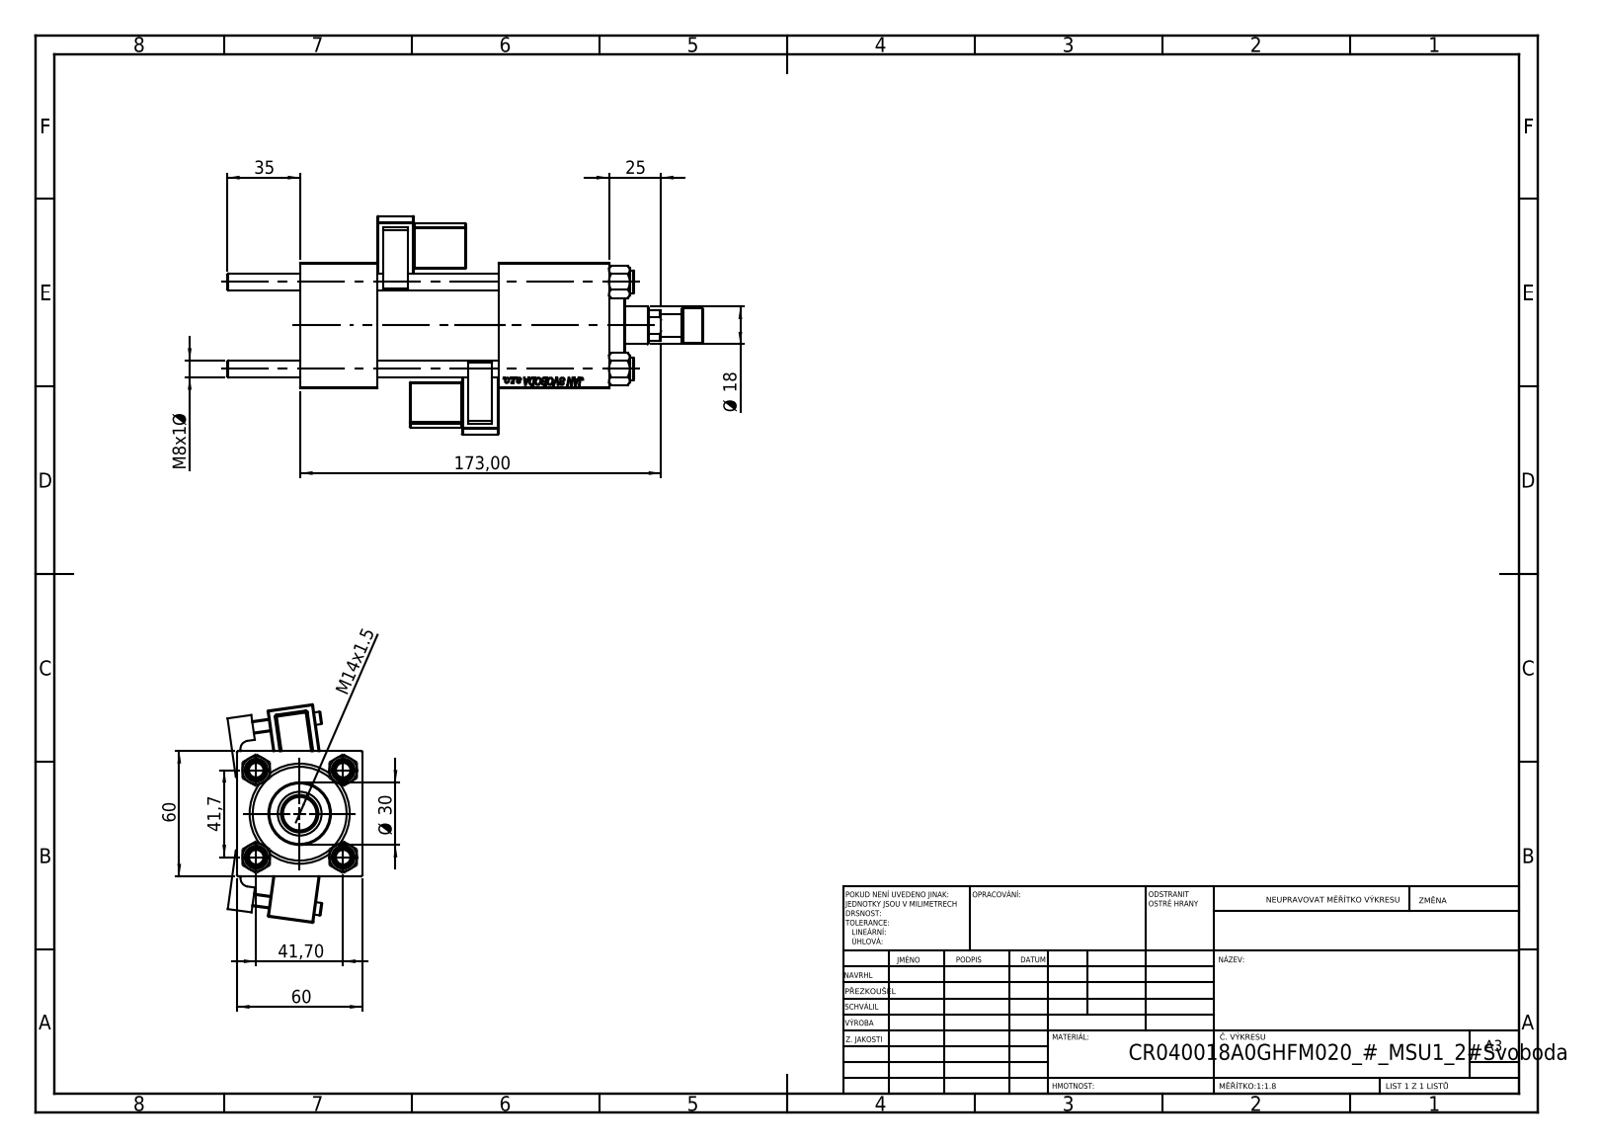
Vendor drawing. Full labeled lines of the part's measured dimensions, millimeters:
Part name (STEP PRODUCT): CR025_012_A_0_G_A_G_M_020_+#_##_TYCINKA; V215CR_MSU; V215CR_ROD_END_F; NUT_M5 (+3 more)
STEP written by: SolidWorks 2019 (CONFIG_CONTROL_DESIGN)
Units: millimetres
Bodies: 14 solids, 1300 faces (582 planar, 142 cylindrical, 576 other)
Overall size (bounding box): 228 × 104.69 × 64.58
Volume: 457 950 mm³ · Surface area: 127 404 mm²
Round holes (diameter × count): ⌀8 ×4, ⌀7 ×2, ⌀16.66 ×2, ⌀24 ×2, ⌀8.5 ×1, ⌀18 ×1, ⌀21 ×1, ⌀31 ×1, ⌀40 ×1, ⌀45 ×1
Round bosses / shafts (diameter × count): ⌀11 ×5, ⌀6 ×2, ⌀46 ×1, ⌀30 ×1, ⌀17 ×1
Partial cylindrical surfaces — rounded edges, fillets, slot ends (radius × count): R0.5 ×48, R1 ×2, R2.5 ×2, R4 ×2
Main face-to-face distances: 60, 37, 58, 53, 148, 111, 95, 119.3, 82.3, 24.3
Hole centre spacings: 29.49, 41.7, 58.97, 92.5
